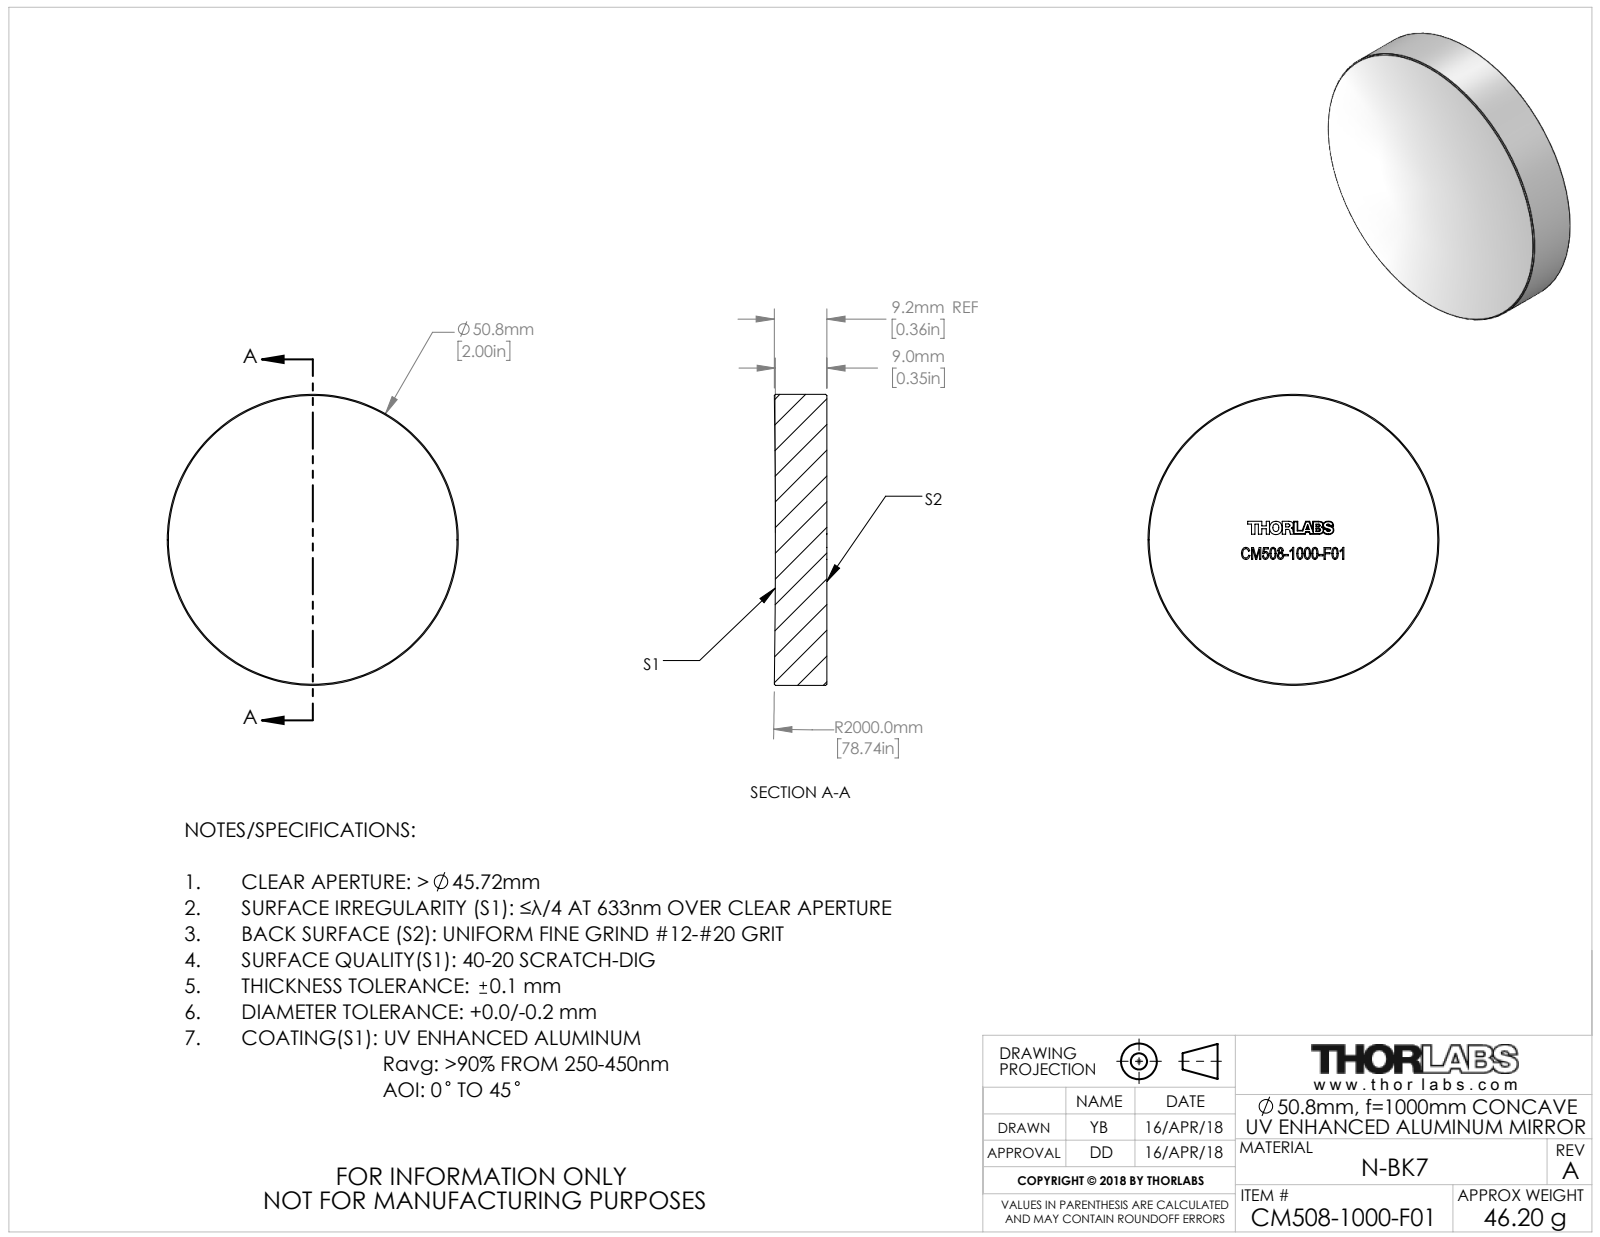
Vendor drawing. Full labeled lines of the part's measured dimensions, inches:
Part name (STEP PRODUCT): TTN153336-E0W
STEP written by: SolidWorks 2018 (CONFIG_CONTROL_DESIGN)
Units: inches
Bodies: 1 solid, 45 faces (37 planar, 2 cylindrical, 6 other)
Overall size (bounding box): 2 × 2 × 0.361
Volume: 1.123 in³ · Surface area: 8.491 in²
Round bosses / shafts (diameter × count): ⌀2 ×1
